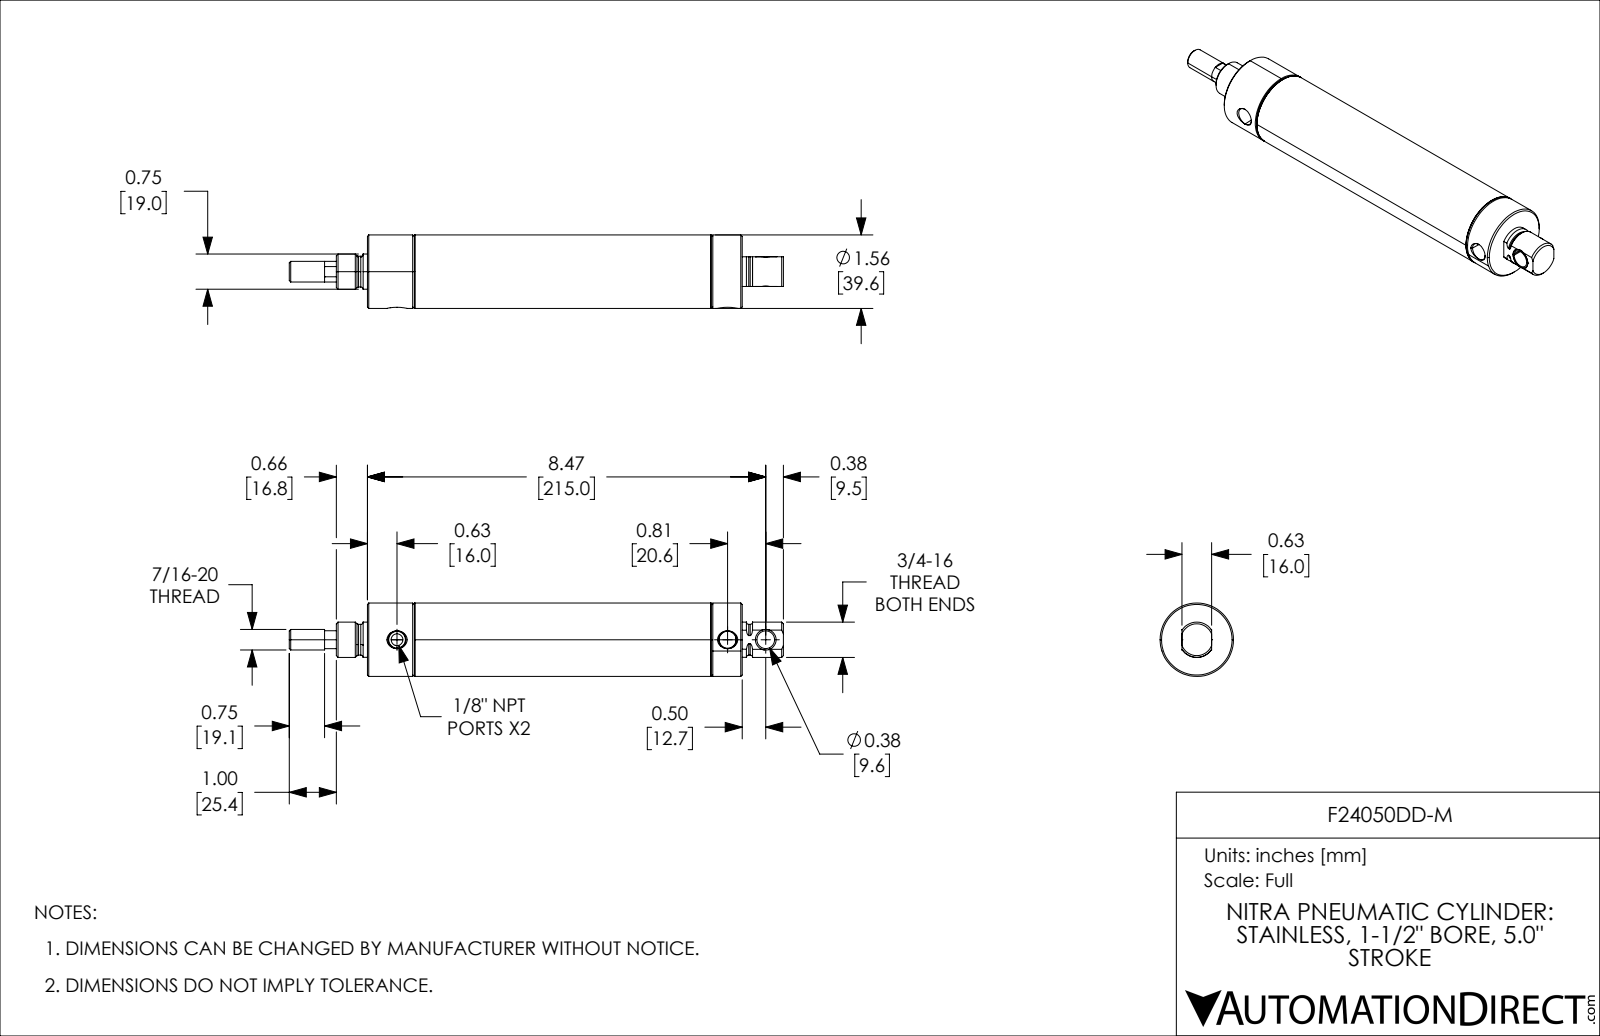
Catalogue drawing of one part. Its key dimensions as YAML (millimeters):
part_name: "F24050DD-M_5; F24050DD-M_7; F24050DD-M_11; F24050DD-M (+2 more)"
step_written_by: "SolidWorks 2021 (CONFIG_CONTROL_DESIGN)"
units: millimeters
bodies: {solids: 5, faces: 157, planar: 35, cylindrical: 58, other: 64}
overall_size: [266.7, 39.62, 39.62]
volume: 117545
surface_area: 71178
round_holes:
  - {diameter: 6.35, count: 1}
  - {diameter: 9.14, count: 1}
  - {diameter: 9.55, count: 1}
  - {diameter: 11.15, count: 1}
  - {diameter: 11.73, count: 1}
  - {diameter: 13.51, count: 1}
  - {diameter: 26.97, count: 1}
  - {diameter: 36.36, count: 1}
round_bosses_or_shafts:
  - {diameter: 39.62, count: 1}
  - {diameter: 38.39, count: 1}
  - {diameter: 19.05, count: 1}
  - {diameter: 18.99, count: 1}
  - {diameter: 16.61, count: 1}
  - {diameter: 16.6, count: 1}
  - {diameter: 11.13, count: 1}
  - {diameter: 11.11, count: 1}
face_to_face_distances: [22.22, 44.45, 127, 149.22, 171.45, 22.23, 30.86, 157.86, 180.08, 202.31]
hole_center_spacings: [20.57, 178.44, 199.01]
